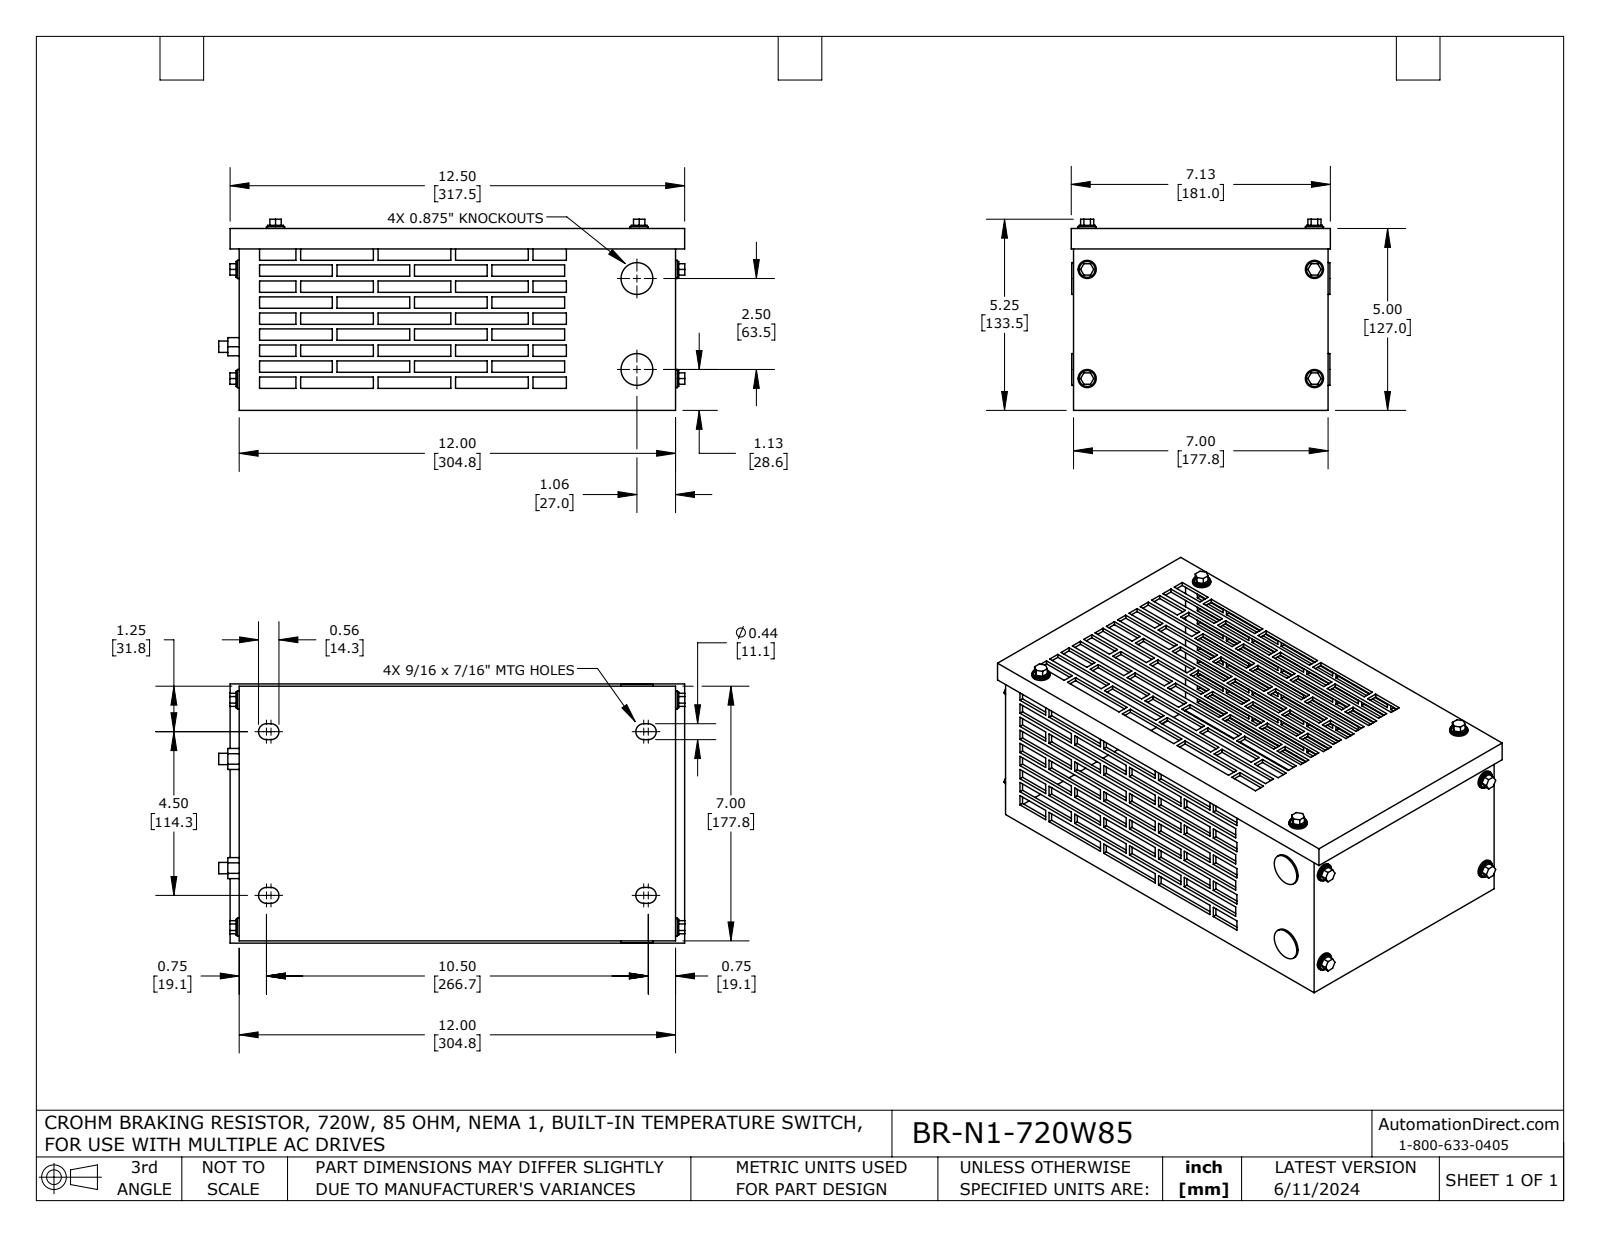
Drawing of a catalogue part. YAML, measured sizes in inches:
part_name: "BR-N1-720W85"
step_written_by: "SolidWorks 2021 (AUTOMOTIVE_DESIGN)"
units: inches
bodies: {solids: 31, faces: 846, planar: 746, cylindrical: 100, other: 0}
overall_size: [12.817, 7.125, 5.254]
volume: 28.59
surface_area: 639.2
round_holes:
  - {diameter: 0.25, count: 8}
  - {diameter: 0.75, count: 2}
round_bosses_or_shafts:
  - {diameter: 0.5, count: 8}
  - {diameter: 0.437, count: 8}
  - {diameter: 0.875, count: 2}
  - {diameter: 0.313, count: 2}
partial_cylinders:
  - {radius: 0.219, count: 8}
face_to_face_distances: [0.1, 4.9, 11.9, 6.9, 5, 4.8, 12, 7, 11.8, 6.8]
hole_center_spacings: [6.25, 3, 6.933, 10, 11.793, 2.5]
